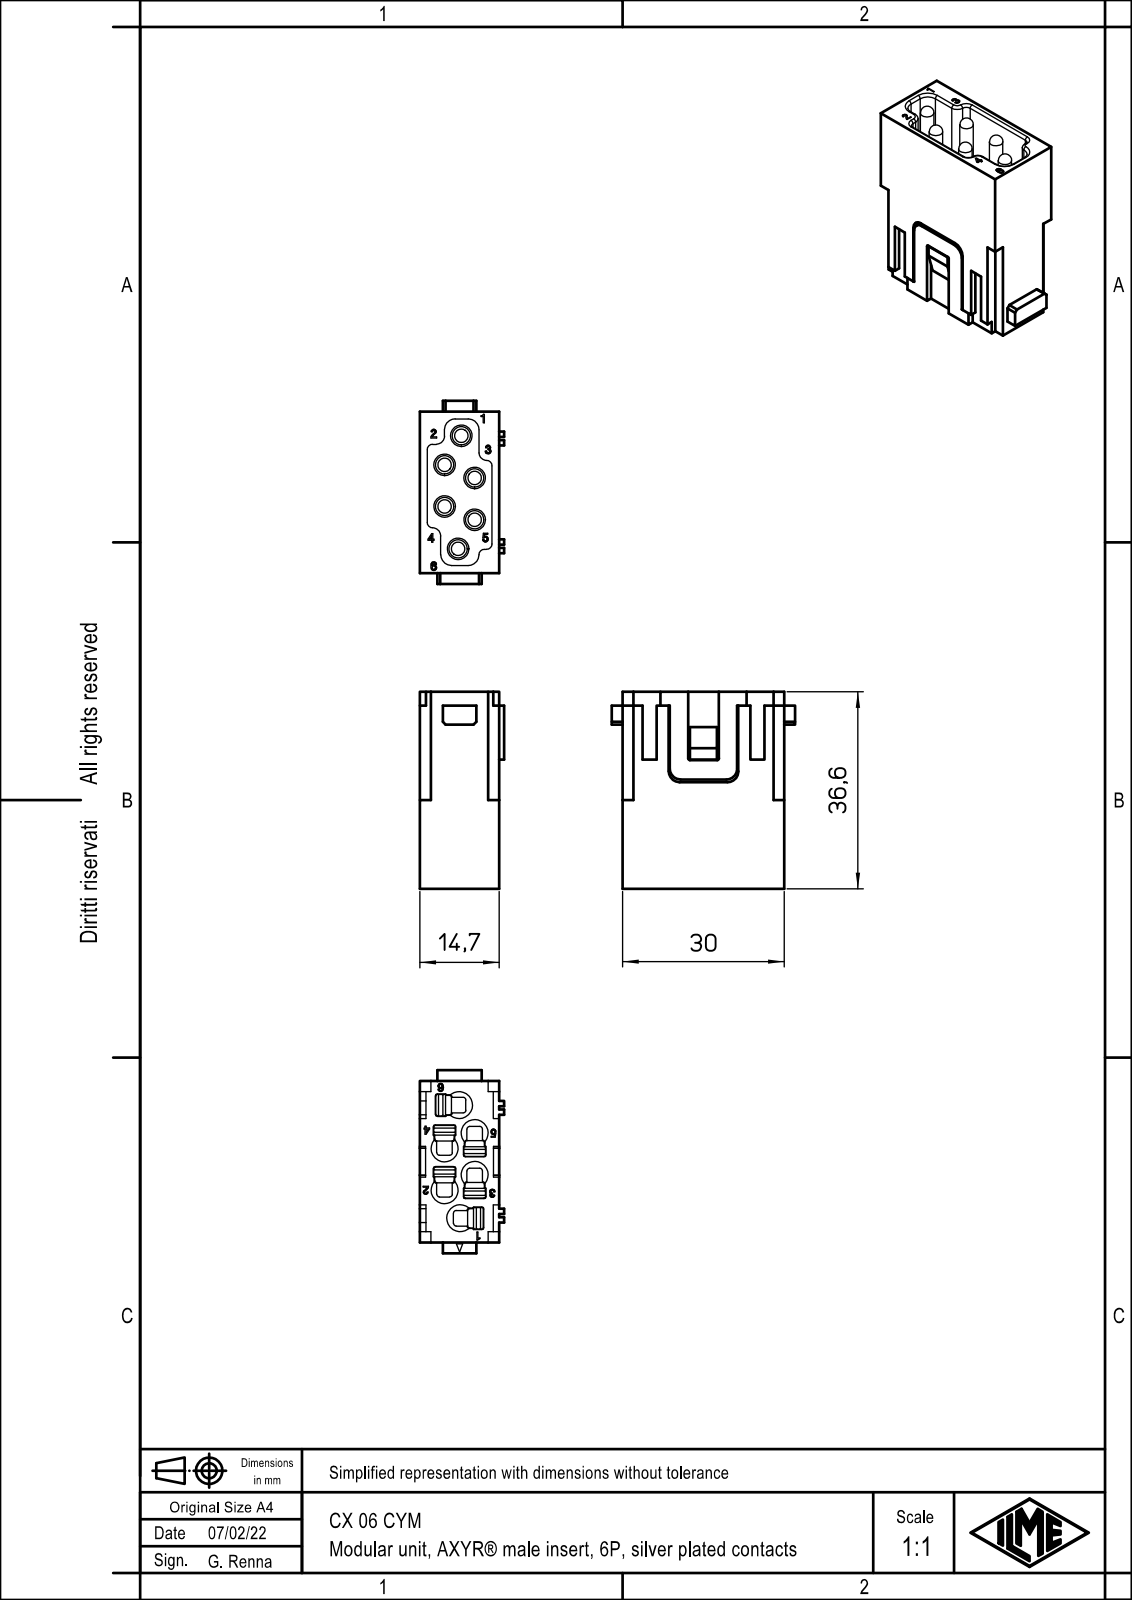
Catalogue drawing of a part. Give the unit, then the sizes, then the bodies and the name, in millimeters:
Units: millimetres
Overall size (bounding box): 36.6 × 34 × 15.6
Round bosses / shafts (diameter × count): ⌀4 ×6, ⌀2.5 ×6
Partial cylindrical surfaces — rounded edges, fillets, slot ends (radius × count): R0.2 ×64, R0.4 ×36, R0.5 ×30, R0.3 ×14, R2 ×14, R0.1 ×12, R2.5 ×6, R1 ×5
Main face-to-face distances: 14.7, 30, 1.35, 13.35, 12, 2, 12.65, 0.7, 0.9, 1.8
Volume: 11 408 mm³ · Surface area: 7 871 mm²
Bodies: 1 solid, 939 faces (591 planar, 240 cylindrical, 108 other)
Part name (STEP PRODUCT): CX_06_CYM
STEP written by: Creo Elements/Direct Modeling 20.1B 02-Apr-2019 (C) Parametric Technology GmbH (AUTOMOTIVE_DESIGN)
